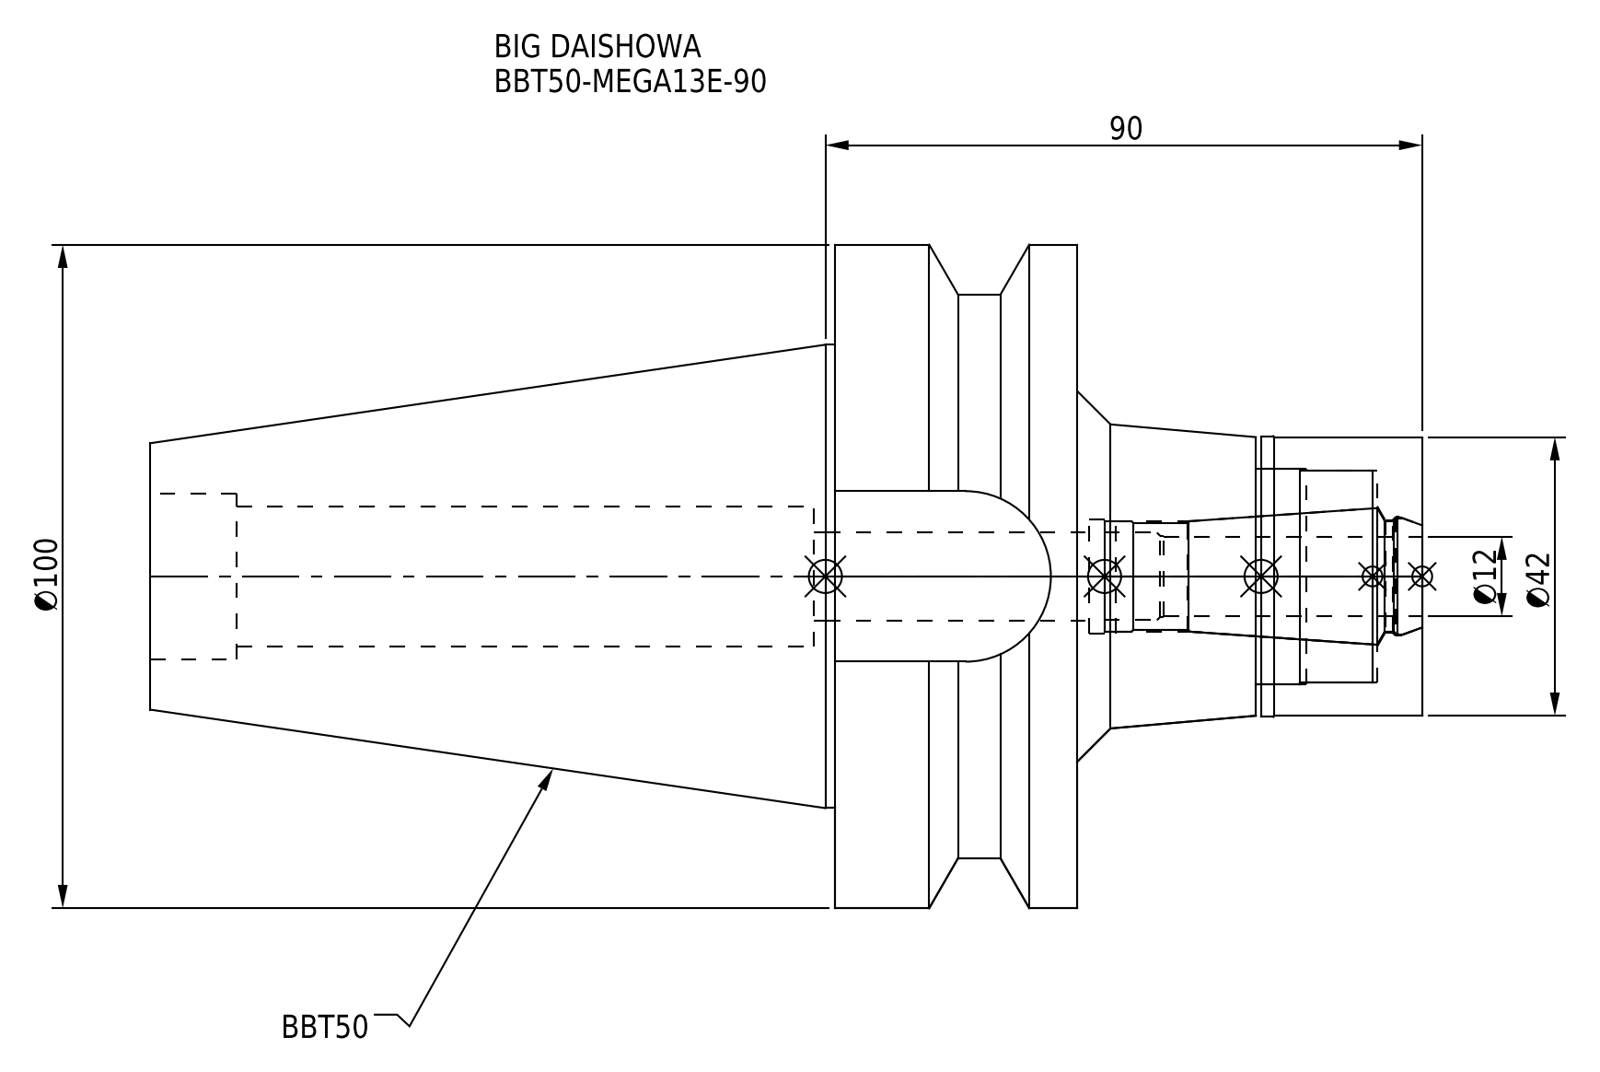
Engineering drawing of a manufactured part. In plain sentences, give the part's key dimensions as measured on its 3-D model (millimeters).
The part is named "BBT50ME13090-120_ASM.stp; BBT50-MEGA13E-90-120.stp; BBT50-MEGA13E-90; MEN13_1.stp (+3 more)". Its 3-D file was written by "SolidWorks 2019 (CONFIG_CONTROL_DESIGN)". It is 2 solids with 78 faces: 20 planar, 38 cylindrical and 20 other. Overall it measures 191.8 by 100 by 100 millimeters. Its volume is 520 826 cubic millimeters and its surface area 68 539 square millimeters. Round holes: 1 of diameter 13.3, 1 of diameter 16.6, 1 of diameter 17, 1 of diameter 17.2, 1 of diameter 17.9, 1 of diameter 21.2, 1 of diameter 25, 1 of diameter 32, 1 of diameter 32.5. Round bosses or shafts: 1 of diameter 100, 1 of diameter 85, 1 of diameter 69.85, 1 of diameter 42.3, 1 of diameter 42. Partial cylindrical surfaces (rounded edges, fillets, slot ends): 1 of radius 12.85. The main face-to-face distances are 36.5, 52, 88.5, 191.8, 139.8, 103.3, 70.8, 25.1, 27.7, 24.3.
